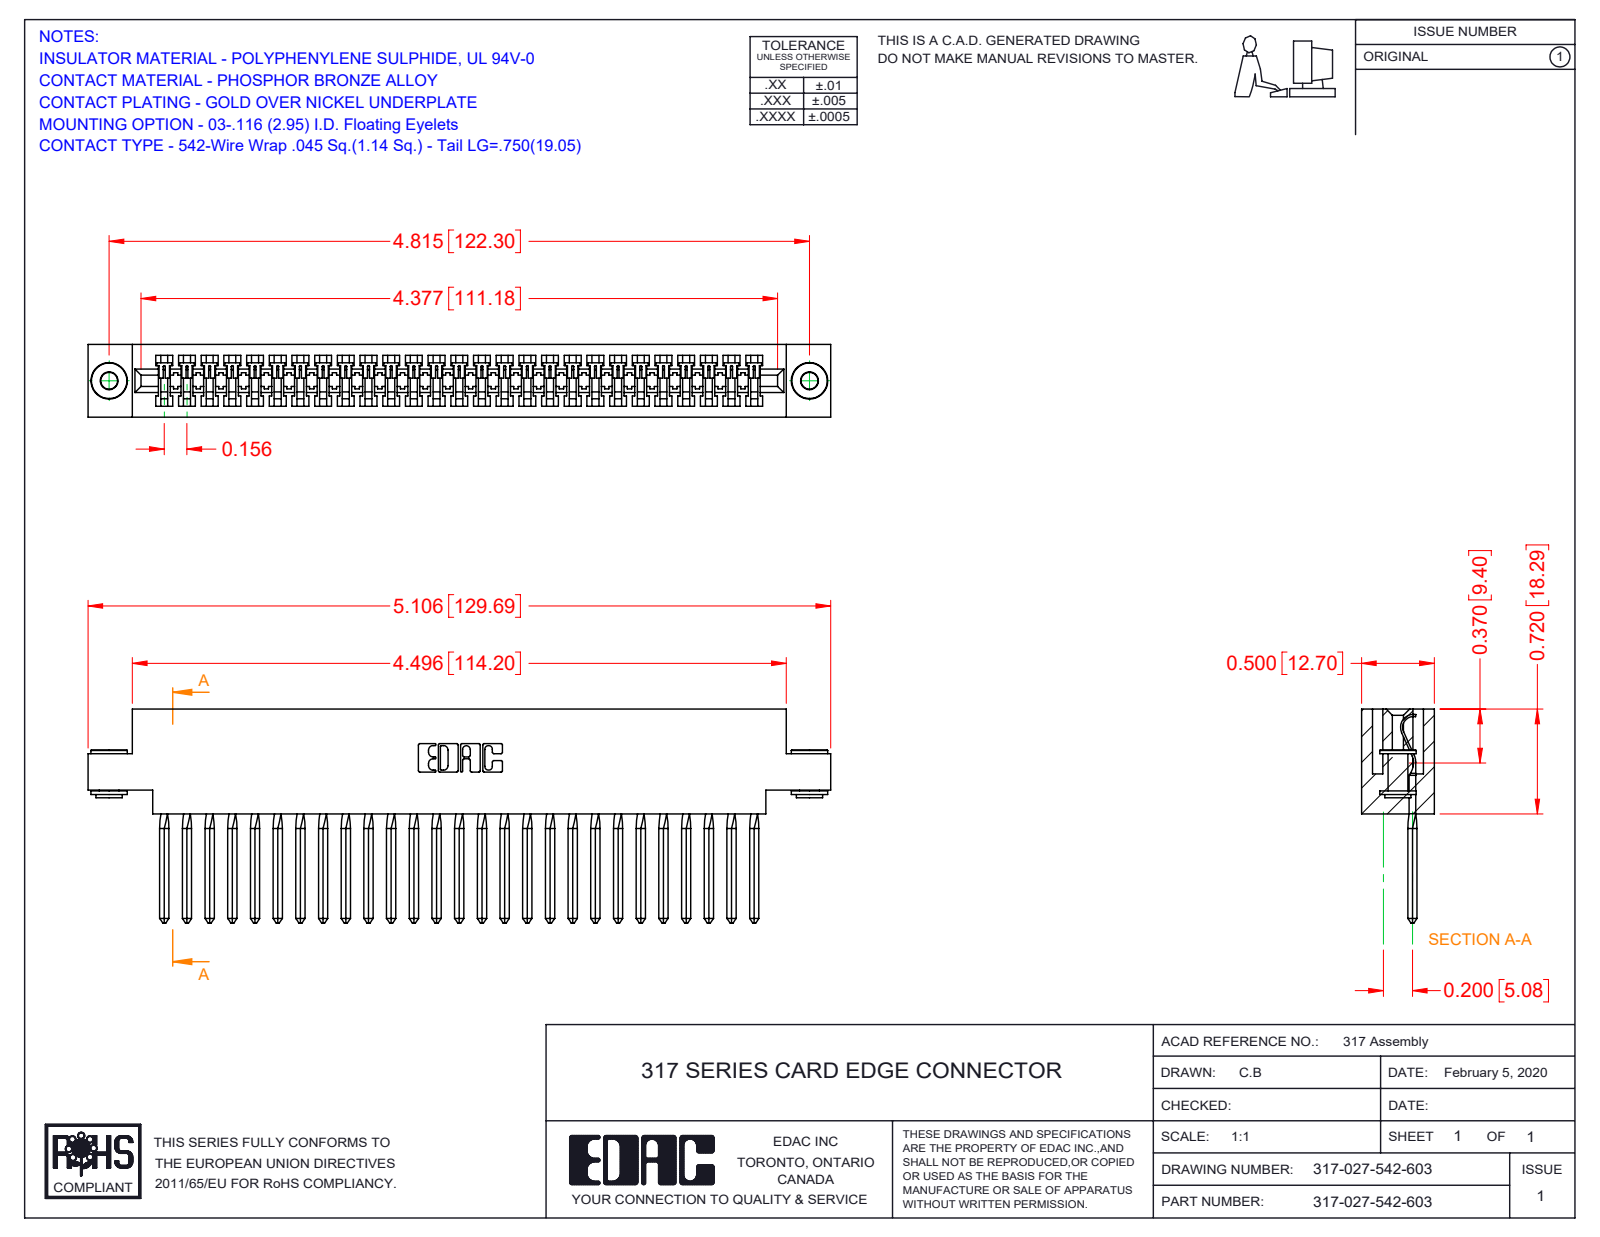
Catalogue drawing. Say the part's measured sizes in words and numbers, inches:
The part is named "345-250-002_345-250-002-102; 317-027-542-603; 317-290-003_542; 317 Part_.156 Dia - TH". Its 3-D file was written by "SolidWorks 2016 (CONFIG_CONTROL_DESIGN)". It is 30 solids with 2165 faces: 1796 planar, 253 cylindrical and 116 other. Overall it measures 5.106 by 1.47 by 0.5 inches. Its volume is 1.199 cubic inches and its surface area 36.99 square inches. Round holes: 2 of diameter 0.116, 2 of diameter 0.156. Round bosses or shafts: 2 of diameter 0.25, 2 of diameter 0.18, 2 of diameter 0.136. Partial cylindrical surfaces (rounded edges, fillets, slot ends): 54 of radius 0.006, 22 of radius 0.01, 6 of radius 0.007, 6 of radius 0.031, 3 of radius 0.026, 1 of radius 0.074, 1 of radius 0.089, 1 of radius 0.1. The main face-to-face distances are 0.5, 0.075, 0.425, 0.35, 0.11, 0.72, 0.136, 0.279, 0.211, 0.289. The hole center spacings are 4.815.
